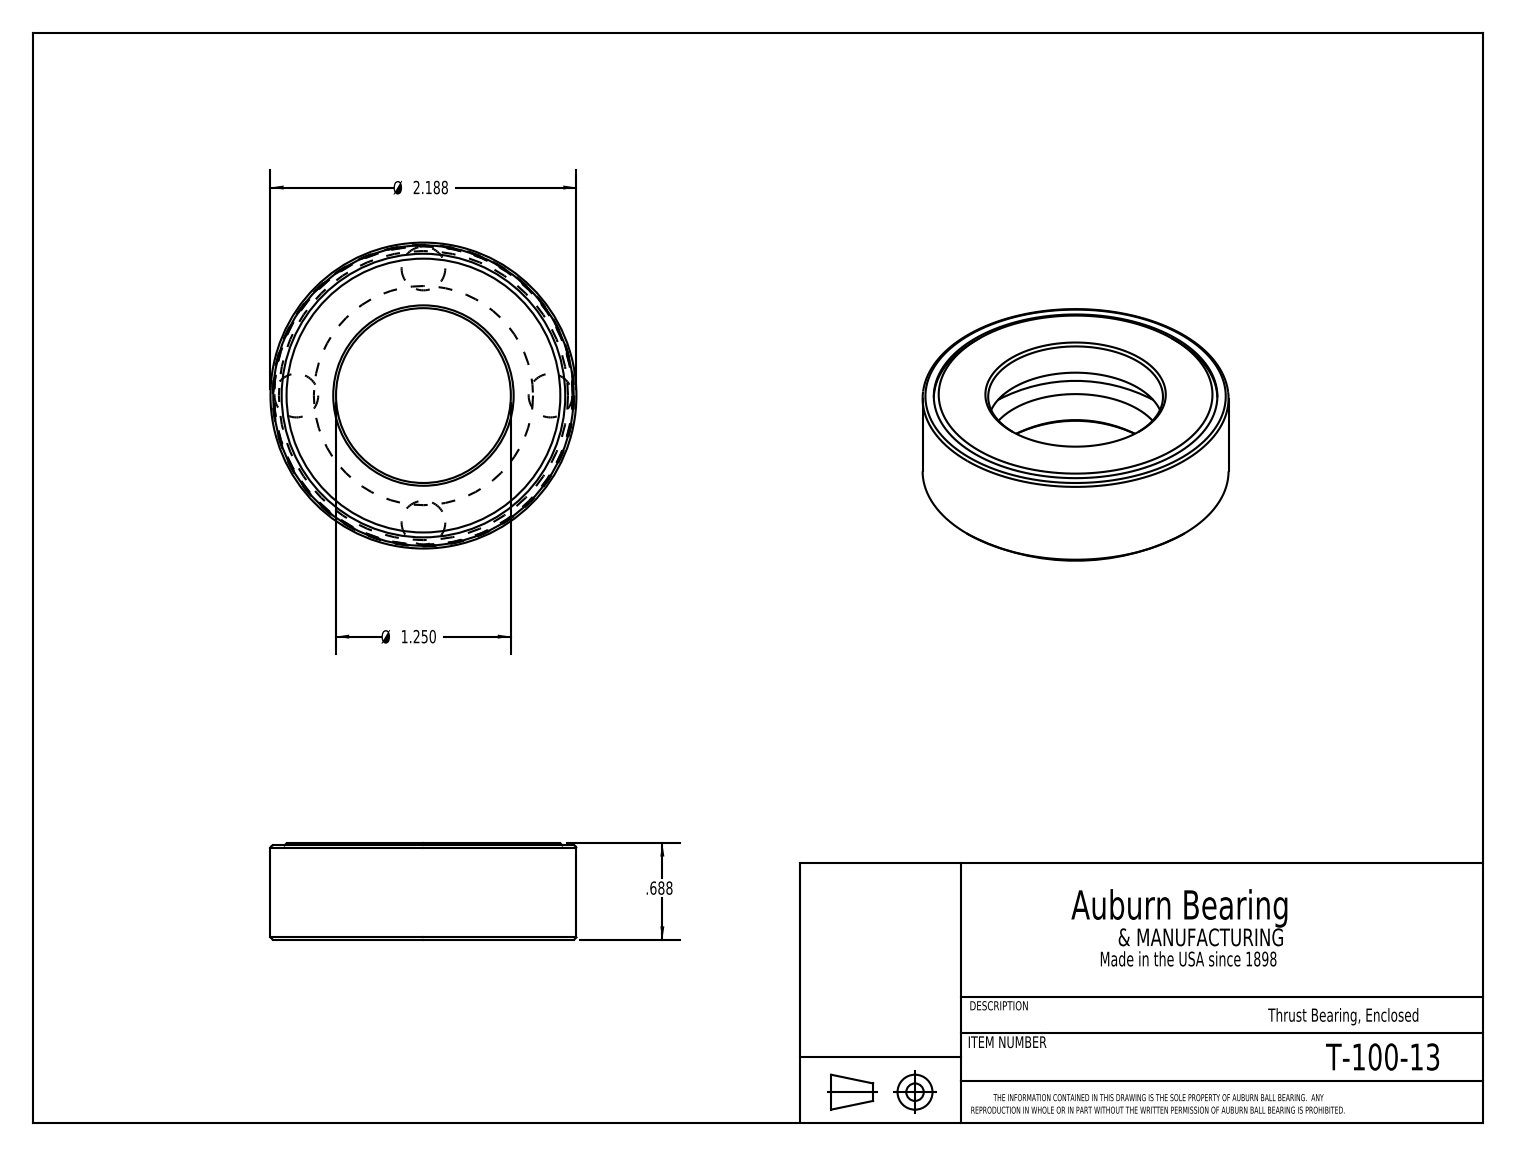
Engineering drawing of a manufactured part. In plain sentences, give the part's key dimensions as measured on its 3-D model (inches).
The part is named "T-100-13". Its 3-D file was written by "SolidWorks 2016 (CONFIG_CONTROL_DESIGN)". It is 6 solids with 28 faces: 9 planar, 7 cylindrical and 12 other. Overall it measures 2.188 by 2.188 by 0.688 inches. Its volume is 1.196 cubic inches and its surface area 22.81 square inches. Round holes: 1 of diameter 1.25, 1 of diameter 2.027, 1 of diameter 2.147. Round bosses or shafts: 1 of diameter 2.187, 1 of diameter 2.133. The main face-to-face distances are 0.25, 0.437, 0.687, 0.187, 0.672, 0.422, 0.235, 0.015, 0.652, 0.402.
